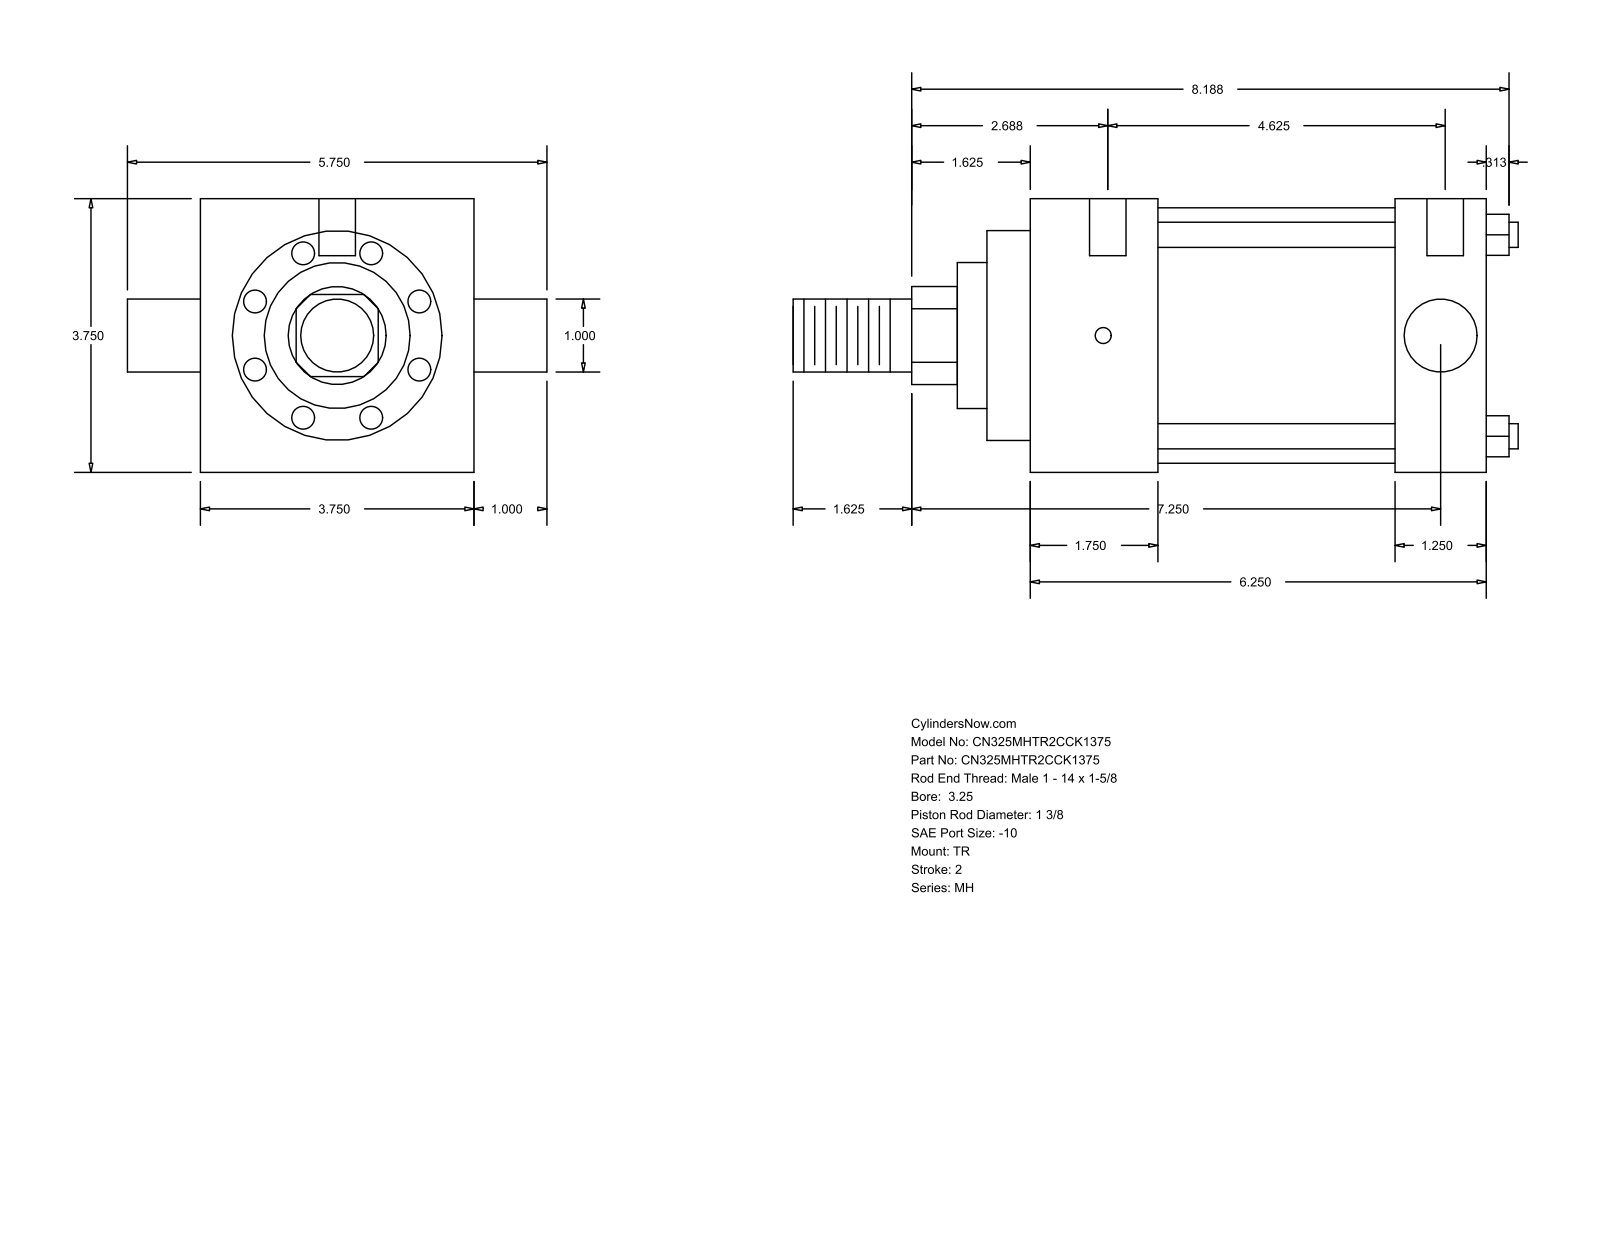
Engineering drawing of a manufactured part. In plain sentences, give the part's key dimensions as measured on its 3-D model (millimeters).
The part is named "MH_TR__0325_1.375". Its 3-D file was written by "GSSL Pune (CONFIG_CONTROL_DESIGN)". It is 0 solids with 86 faces: 61 planar, 25 cylindrical and 0 other. Overall it measures 252.41 by 146.05 by 95.25 millimeters. Round holes: 3 of diameter 5.56, 2 of diameter 12.7. Round bosses or shafts: 4 of diameter 8.76, 2 of diameter 25.4, 1 of diameter 88.9, 1 of diameter 73.03, 1 of diameter 50.8, 1 of diameter 34.92. Partial cylindrical surfaces (rounded edges, fillets, slot ends): 1 of radius 17.06. The main face-to-face distances are 95.24, 158.76, 44.45, 127.01, 82.56, 114.31, 31.75, 15.08, 59.53, 142.09. The hole center spacings are 1.59, 4.76, 117.48, 119.07, 122.24, 123.83.
